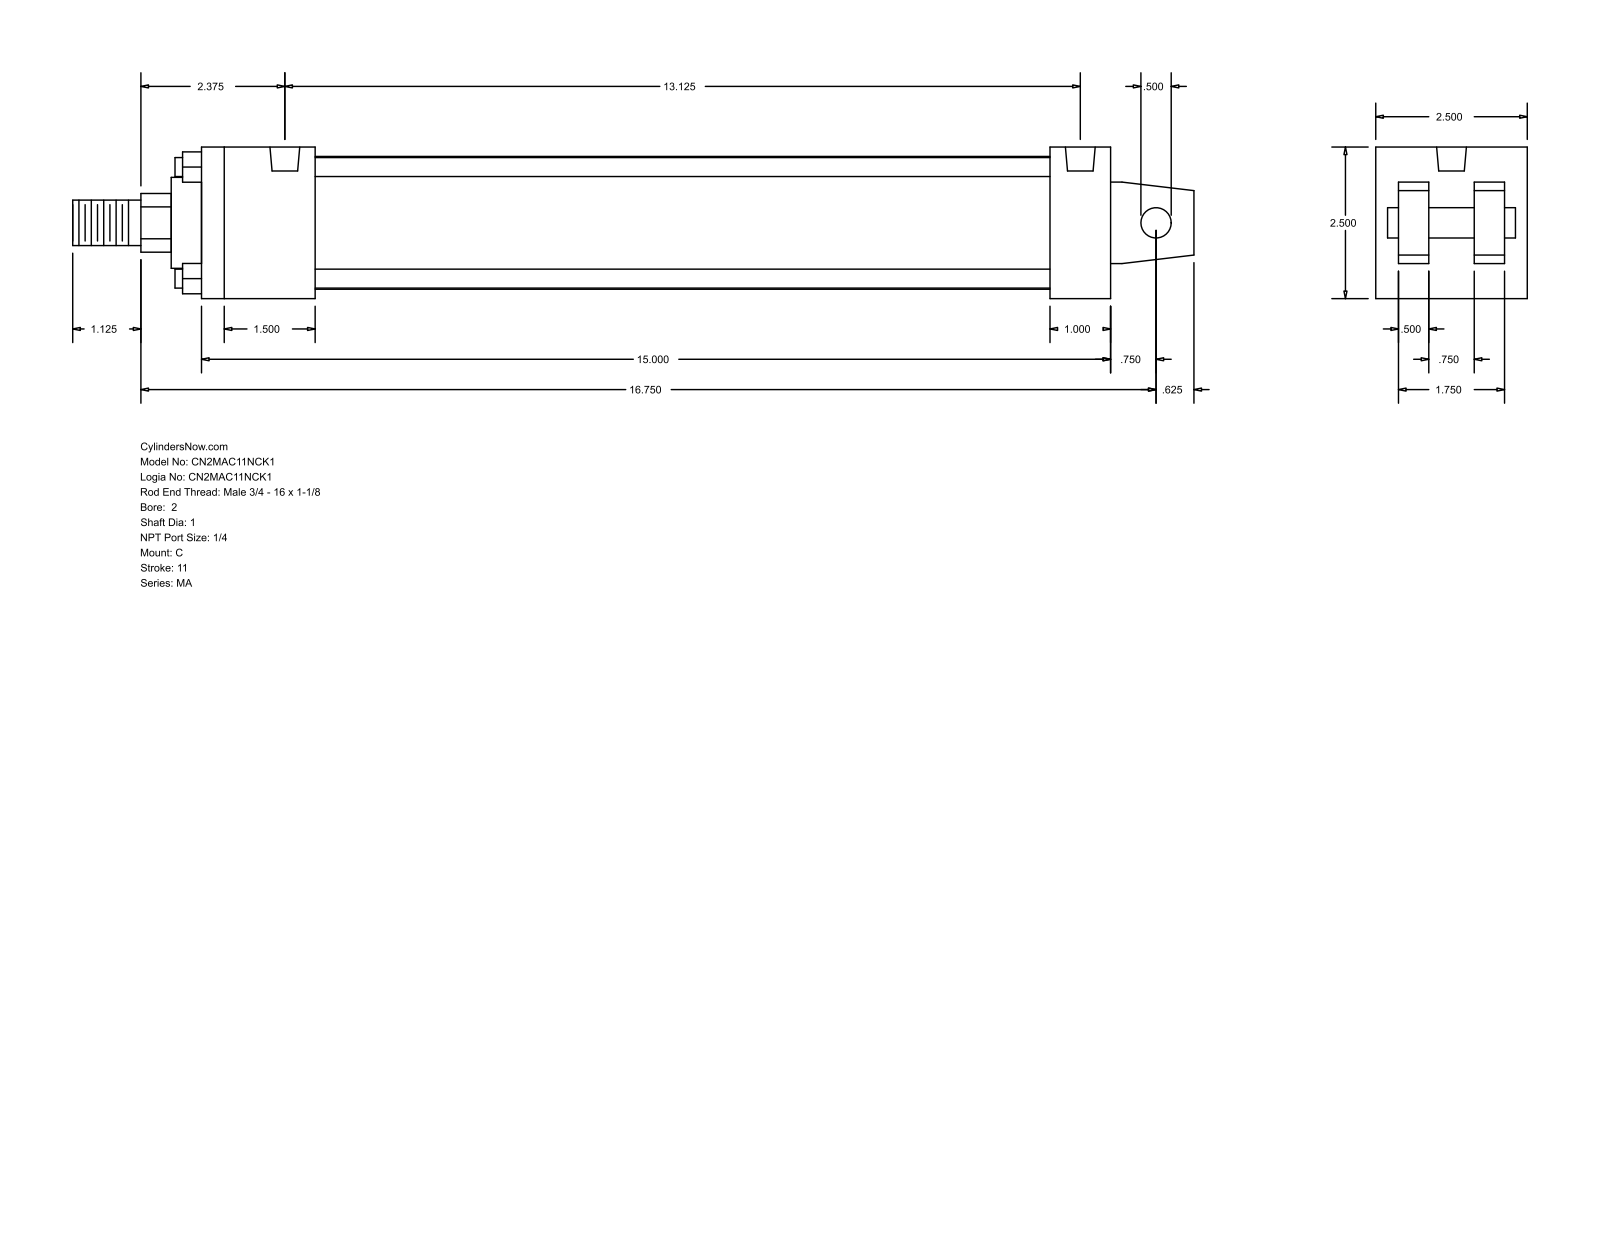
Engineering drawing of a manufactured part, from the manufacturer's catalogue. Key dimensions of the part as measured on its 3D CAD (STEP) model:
Part name (STEP PRODUCT): MA_C__0200_1
STEP written by: GSSL Pune (CONFIG_CONTROL_DESIGN)
Units: millimetres
Bodies: 0 solids, 103 faces (76 planar, 27 cylindrical, 0 other)
Overall size (bounding box): 469.9 × 63.5 × 63.5
Round holes (diameter × count): ⌀7.94 ×4, ⌀12.49 ×2
Round bosses / shafts (diameter × count): ⌀7.94 ×4, ⌀55.63 ×1, ⌀38.1 ×1, ⌀25.4 ×1, ⌀19.05 ×1, ⌀12.7 ×1
Partial cylindrical surfaces — rounded edges, fillets, slot ends (radius × count): R12.29 ×1
Main face-to-face distances: 63.5, 12.7, 381, 22.22, 41.28, 9.52, 53.98, 31.76, 47.63, 25.4
Hole centre spacings: 333.37
